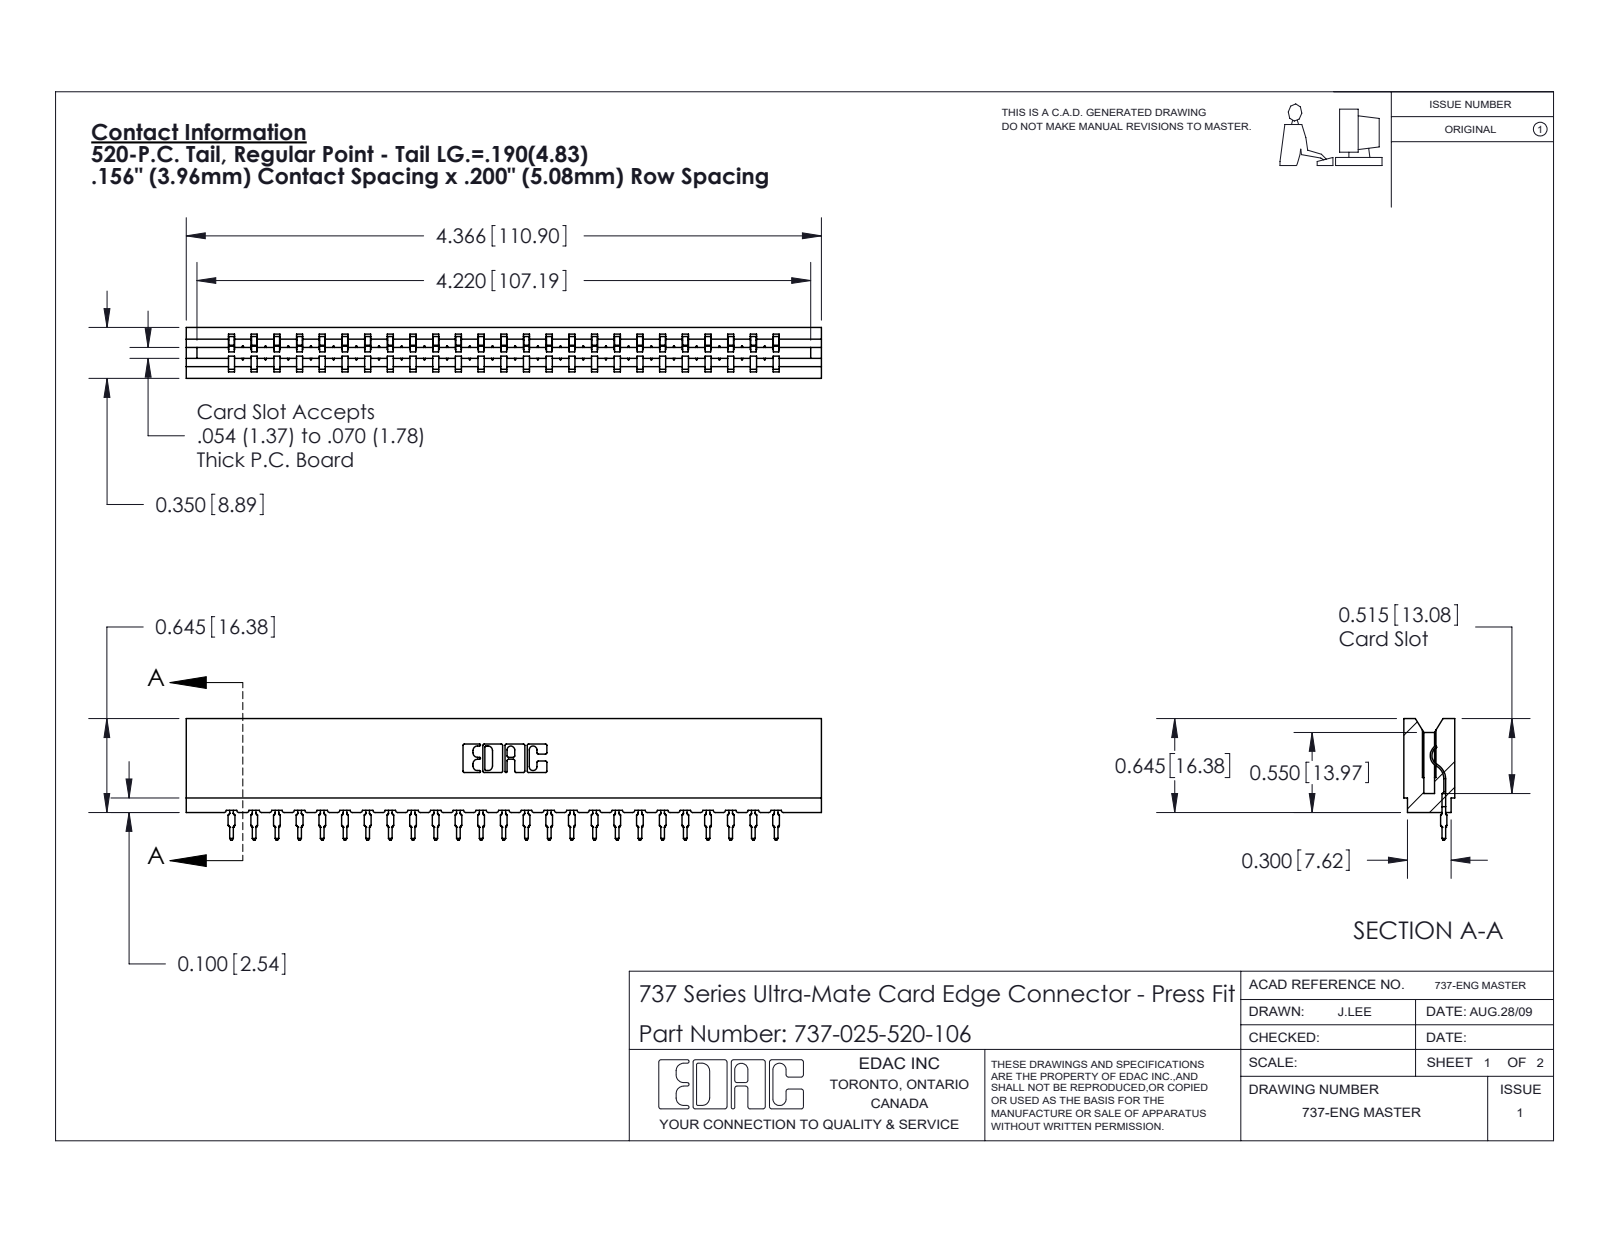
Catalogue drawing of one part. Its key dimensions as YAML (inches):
part_name: "737-025-520-106; 737 Part_Insulator Option - 06; 745-292-001_520"
step_written_by: "SolidWorks 2020 (CONFIG_CONTROL_DESIGN)"
units: inches
bodies: {solids: 26, faces: 2920, planar: 1755, cylindrical: 515, other: 650}
overall_size: [4.366, 0.836, 0.35]
volume: 0.658
surface_area: 21.72
partial_cylinders:
  - {radius: 0.015, count: 50}
  - {radius: 0.021, count: 50}
  - {radius: 0.01, count: 22}
  - {radius: 0.007, count: 6}
  - {radius: 0.031, count: 6}
  - {radius: 0.005, count: 4}
  - {radius: 0.011, count: 4}
  - {radius: 0.026, count: 3}
face_to_face_distances: [0.138, 0.212, 0.35, 0.156, 0.074, 0.624, 0.045, 0.305, 0.093, 0.167]
